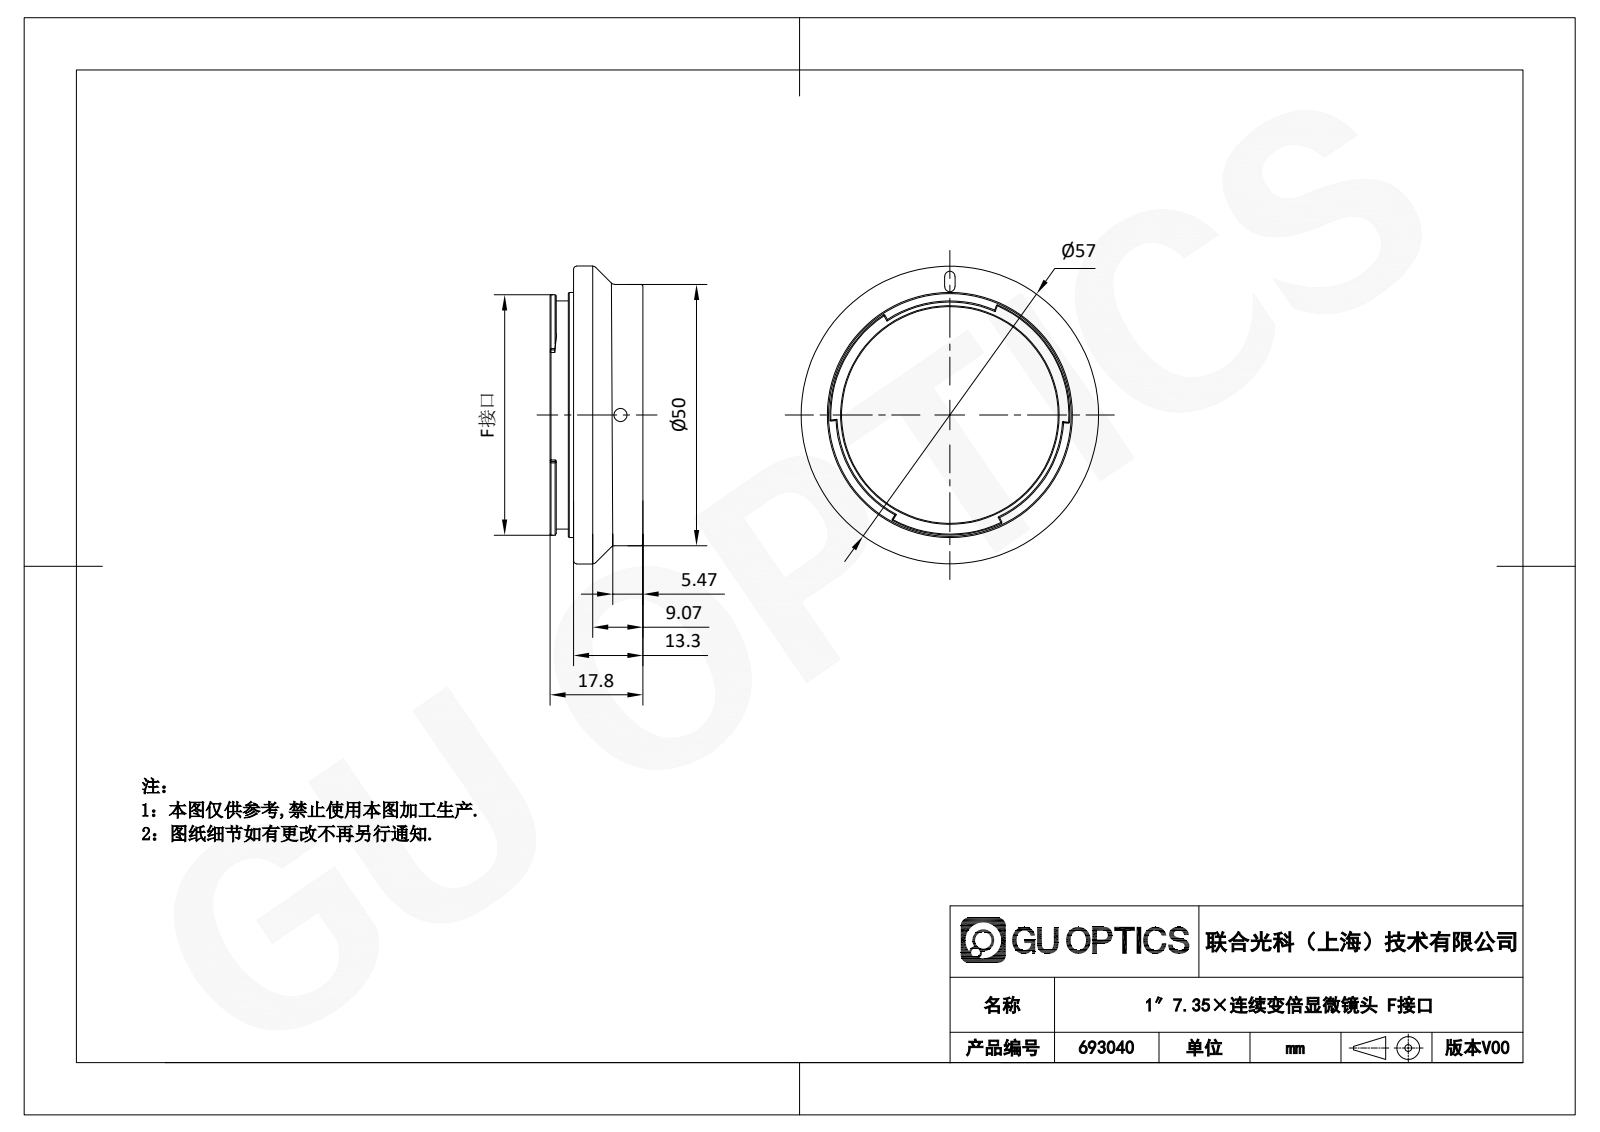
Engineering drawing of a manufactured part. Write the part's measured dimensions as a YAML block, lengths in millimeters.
part_name: "693040"
step_written_by: "SolidWorks 2020 (CONFIG_CONTROL_DESIGN)"
units: millimeters
bodies: {solids: 1, faces: 106, planar: 48, cylindrical: 28, other: 30}
overall_size: [57, 57, 17.8]
volume: 9632
surface_area: 7860
round_holes:
  - {diameter: 2.5, count: 3}
  - {diameter: 1.1, count: 1}
  - {diameter: 2, count: 1}
  - {diameter: 41.5, count: 1}
  - {diameter: 44.8, count: 1}
round_bosses_or_shafts:
  - {diameter: 57, count: 1}
  - {diameter: 50, count: 1}
  - {diameter: 46.9, count: 1}
  - {diameter: 43.7, count: 1}
partial_cylinders:
  - {radius: 1, count: 2}
  - {radius: 23, count: 1}
face_to_face_distances: [0.41, 0.82, 13.3, 1.23, 2.3, 1.64, 2.05, 1, 14.3, 12]
